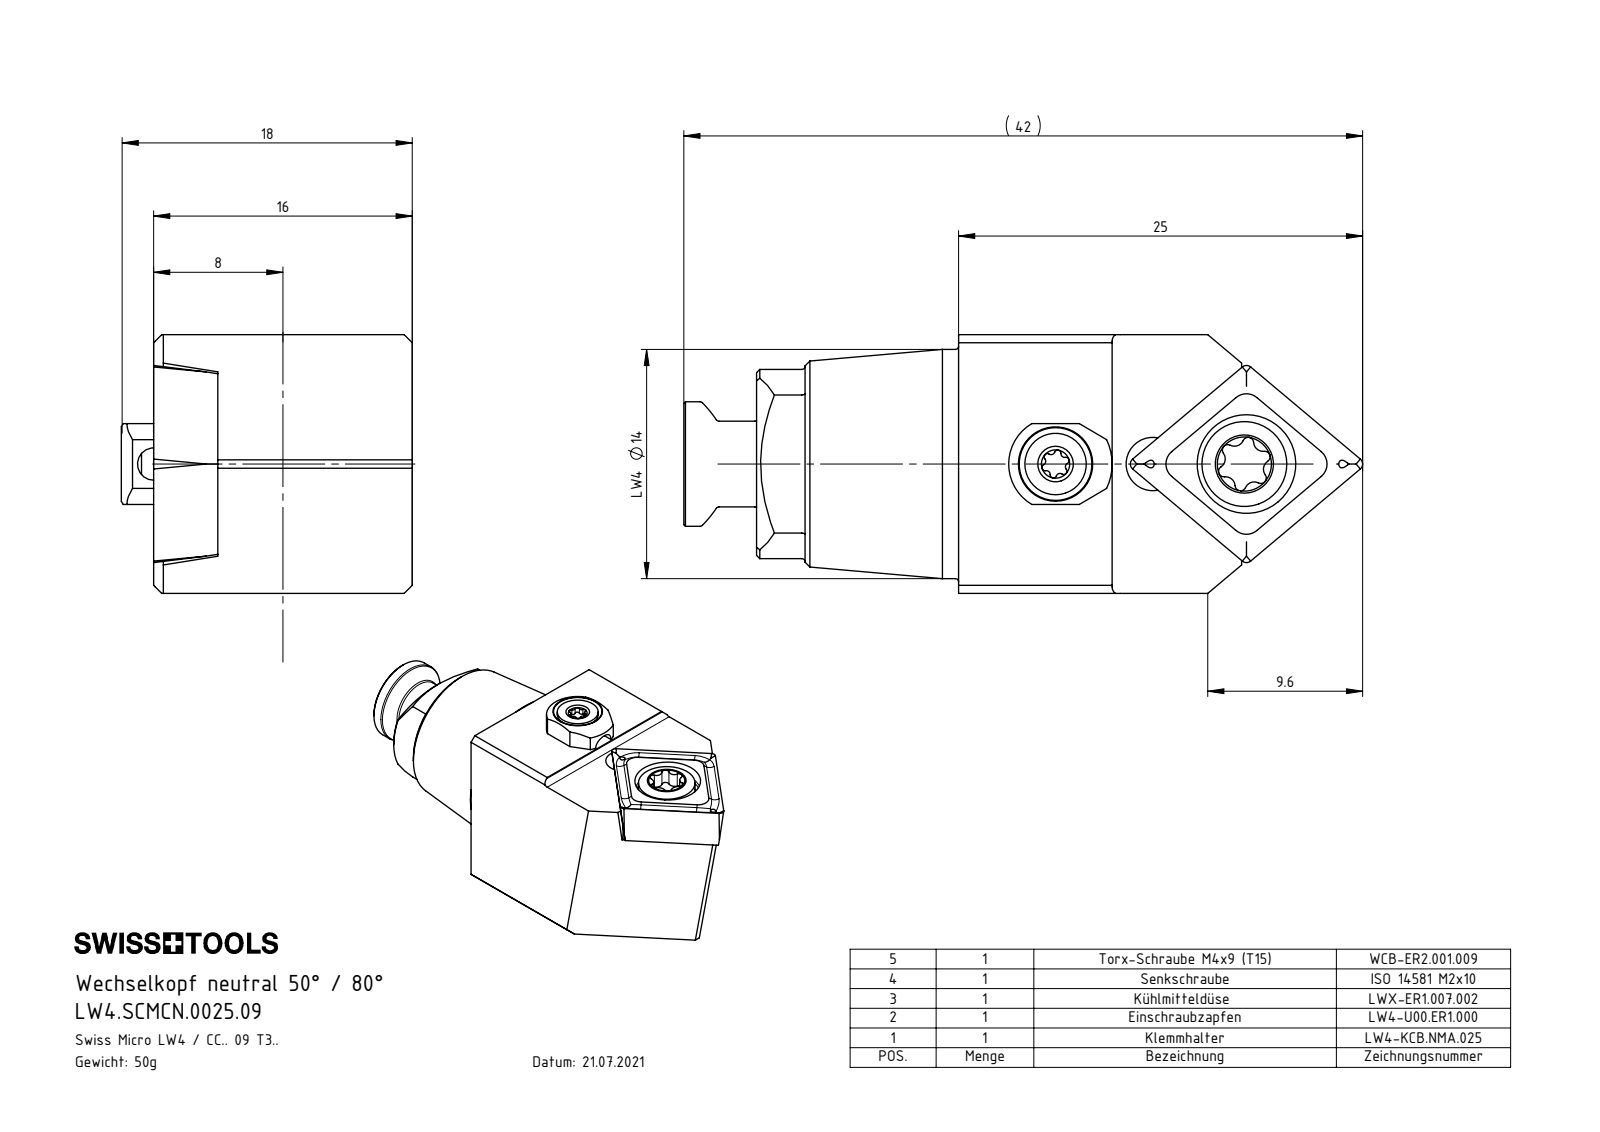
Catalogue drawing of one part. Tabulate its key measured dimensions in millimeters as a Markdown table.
| quantity | value |
| --- | --- |
| part name | LW4-KCB.NMA.025_A; LW4.SCMCN.0025.09; LW4-U00.ER1.000_B; CCMT09T304 (+3 more) |
| STEP written by | SolidWorks 2022 (CONFIG_CONTROL_DESIGN) |
| units | millimeters |
| bodies | 6 solids, 262 faces (69 planar, 80 cylindrical, 113 other) |
| overall size | 42 × 18 × 16 |
| volume | 6 363 mm³ |
| surface area | 3 675 mm² |
| round holes (diameter × count) | 2 × 2, 3.3 × 2, 1.6 × 1, 2.5 × 1, 3 × 1, 4.4 × 1, 5.5 × 1, 6.1 × 1 |
| round bosses / shafts (diameter × count) | 14.17 × 1, 7.7 × 1, 6 × 1, 5.3 × 1, 5.25 × 1, 5 × 1, 4 × 1, 3.8 × 1 |
| partial cylindrical surfaces (radius × count) | 0.2 × 8, 0.24 × 6, 0.34 × 6, 0.59 × 6, 0.5 × 1, 1 × 1, 2.9 × 1, 3.5 × 1 |
| main face-to-face distances | 16, 12.03, 3.97, 15.4, 3.37, 0.6, 7.5, 2, 3, 12.5 |
| hole center spacings | 5.61, 5.67, 5.8, 11.28, 11.41 |
